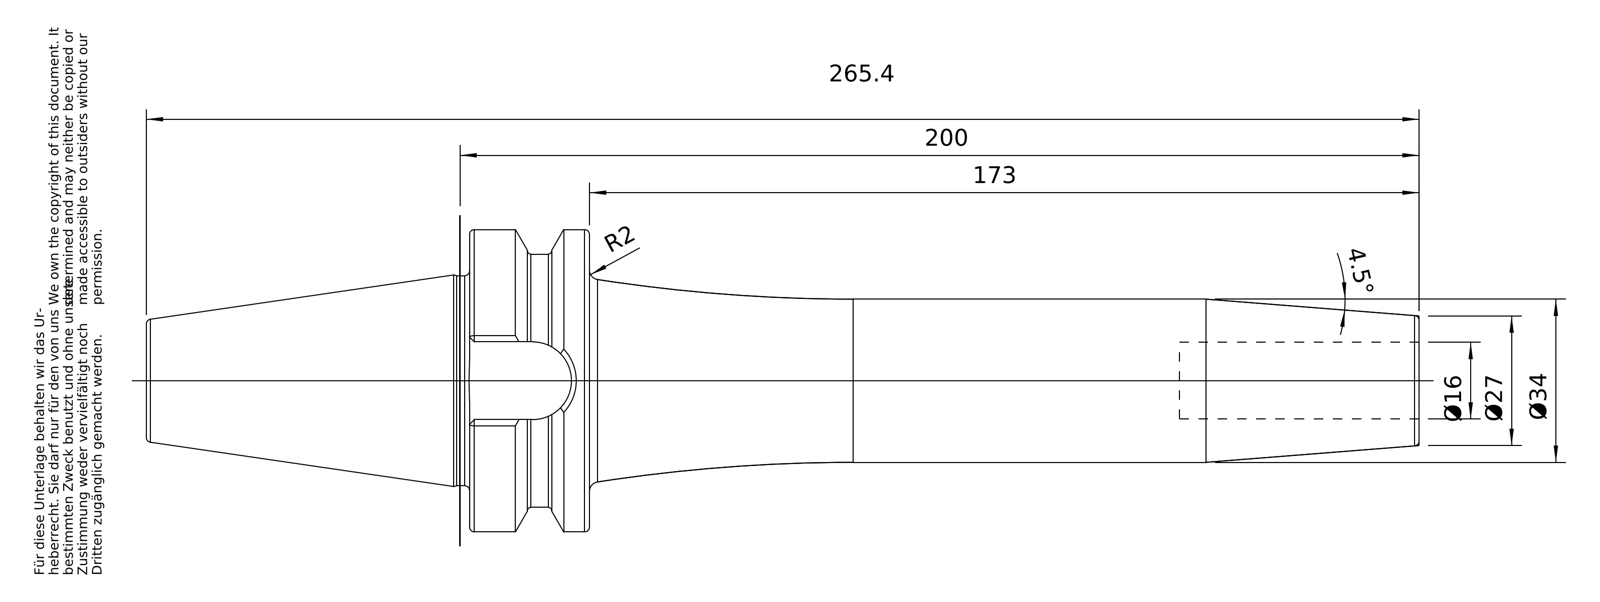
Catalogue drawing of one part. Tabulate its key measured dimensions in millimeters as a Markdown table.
| quantity | value |
| --- | --- |
| part name | 40-646-16 |
| STEP written by | PRO/ENGINEER BY PARAMETRIC TECHNOLOGY CORPORATION, 2010430 (CONFIG_CONTROL_DESIGN) |
| units | millimeters |
| bodies | 1 solid, 98 faces (26 planar, 22 cylindrical, 50 other) |
| overall size | 265.4 × 62.98 × 62.98 |
| volume | 274 628 mm³ |
| surface area | 41 910 mm² |
| round holes (diameter × count) | 13.84 × 1, 16 × 1, 17.01 × 1, 17.5 × 1 |
| round bosses / shafts (diameter × count) | 62.98 × 1, 52.75 × 1, 43.75 × 1, 34 × 1, 16.01 × 1 |
| partial cylindrical surfaces (radius × count) | 8.1 × 1 |
| main face-to-face distances | 25, 44.9, 198, 173, 148, 123, 50, 16.2, 67.4, 92.4 |
